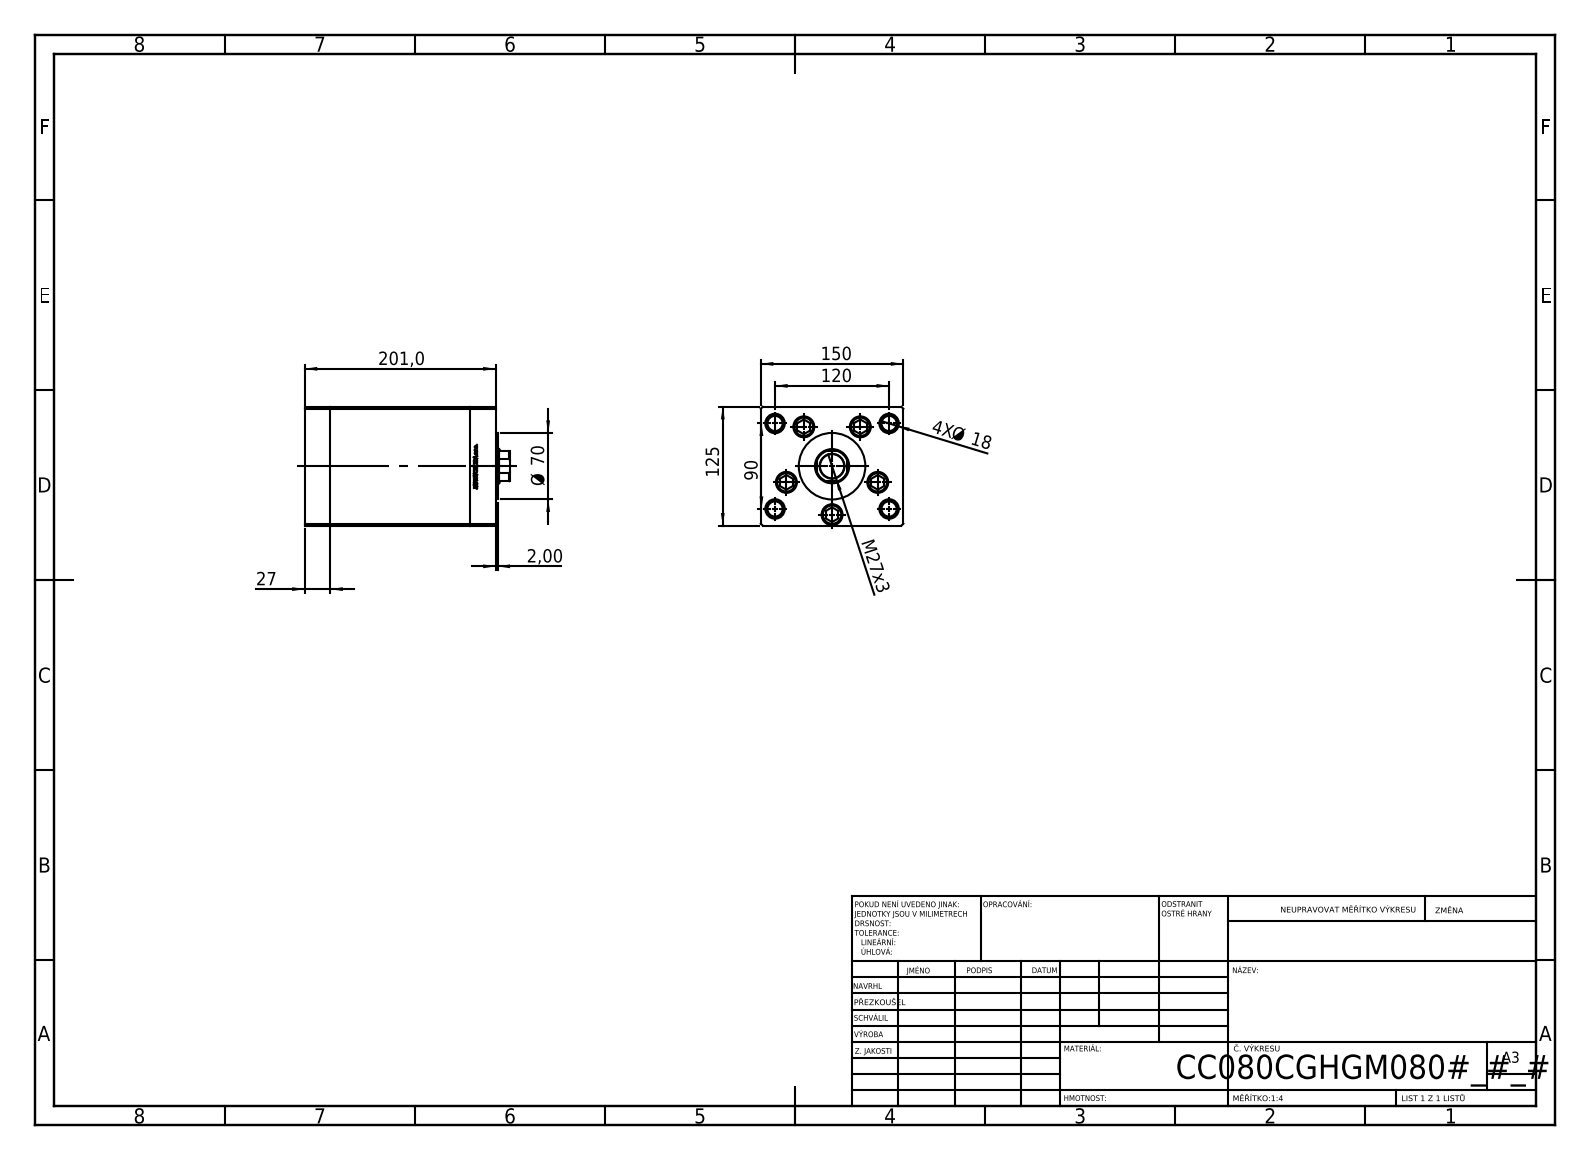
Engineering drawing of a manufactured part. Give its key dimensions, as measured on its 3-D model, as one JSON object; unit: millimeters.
{"part_name": "V220C_VC_C; V220C BACK_C; V220C FRONT; V220C_C MIDDLE (+1 more)", "step_written_by": "SolidWorks 2019 (CONFIG_CONTROL_DESIGN)", "units": "millimeters", "bodies": {"solids": 13, "faces": 1186, "planar": 545, "cylindrical": 179, "other": 462}, "overall_size": [216, 150, 125], "volume_mm3": 3120000, "surface_area_mm2": 380247, "round_holes": [[17.5, 9], [22, 5], [2, 4], [13.16, 4], [16, 4], [20.5, 4], [21, 1], [25.5, 1], [36, 1]], "round_bosses_or_shafts": [[8, 5], [21, 4], [80, 1], [70, 1]], "partial_cylinders_radius": [[0.93, 2], [17.5, 1]], "face_to_face_distances": [27, 174, 147, 125, 150, 33.5, 201, 6.5, 167.5, 140.5], "hole_center_spacings": [51, 75, 30.43, 30.48, 58.89, 60.3, 61.25, 63.14]}
